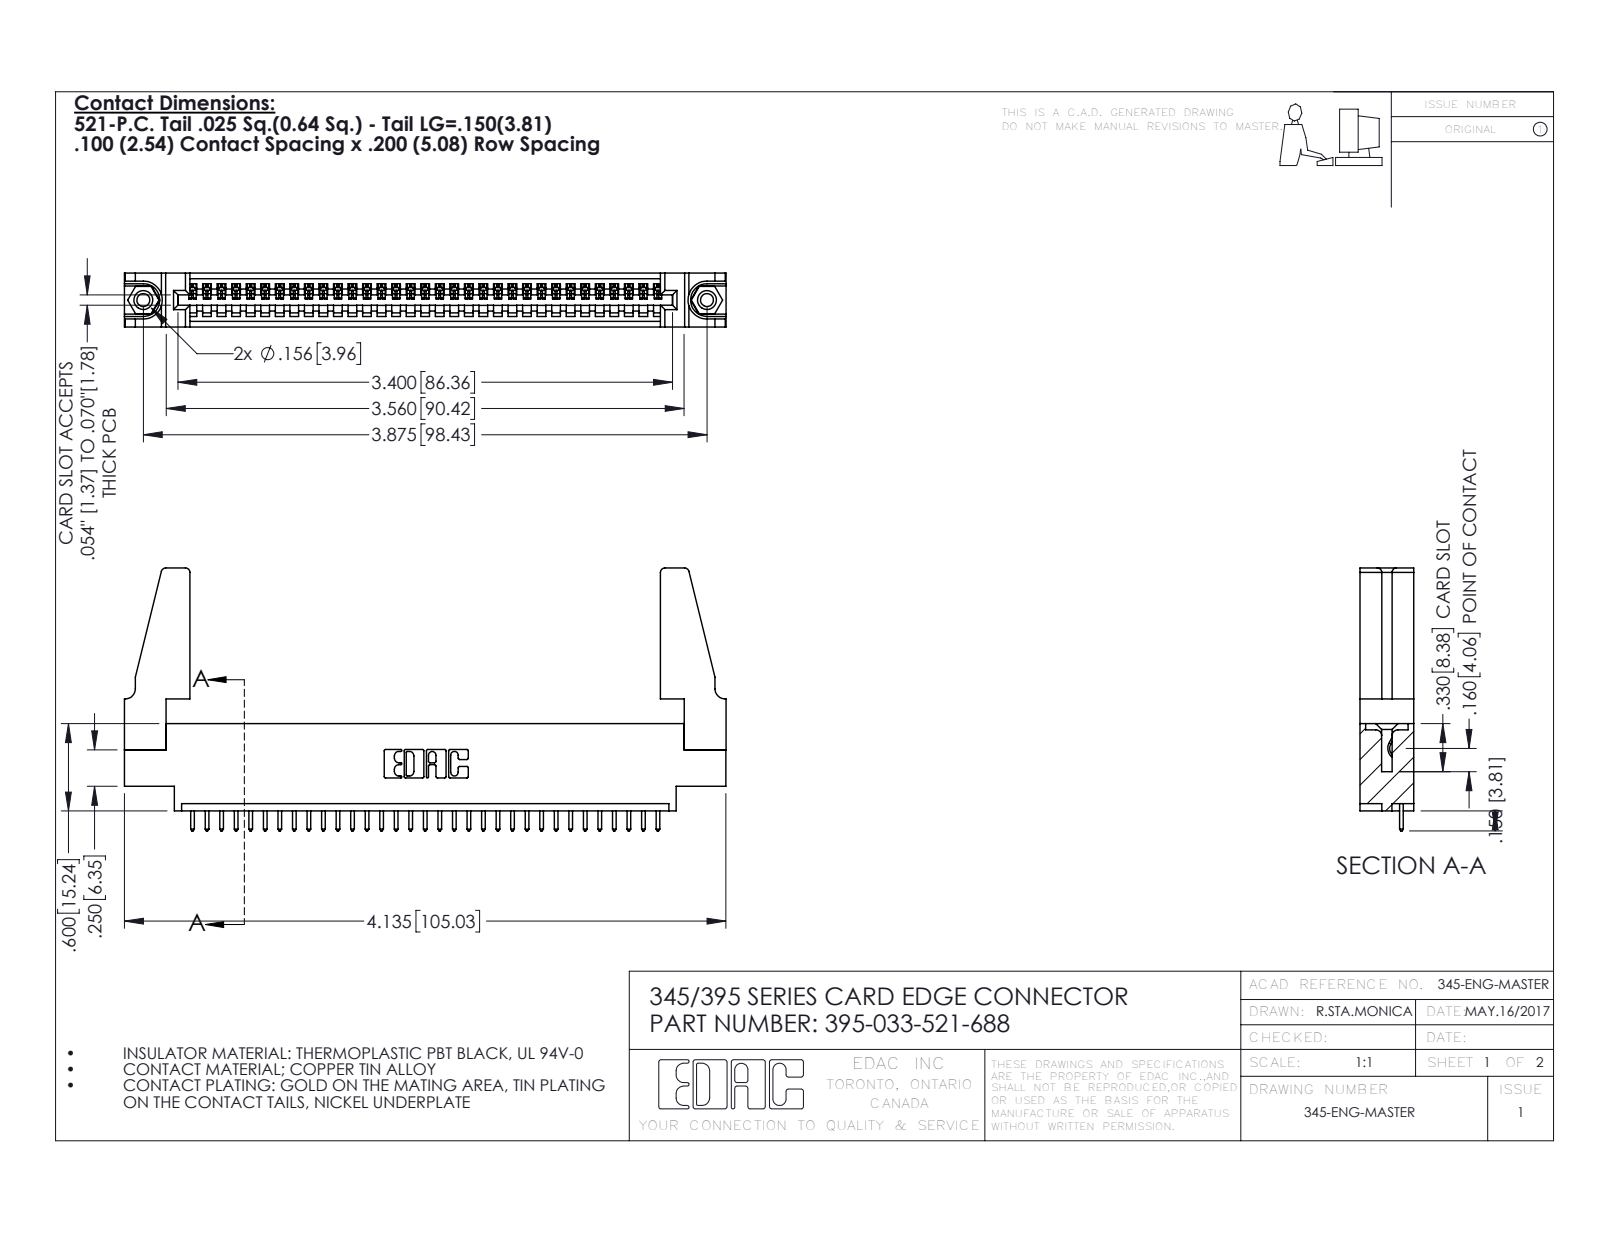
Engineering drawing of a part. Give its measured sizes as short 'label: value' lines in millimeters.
name: 395-033-521-688; 345 Part_0.170 Offset - 0.156 Dia-TH; 345-220-078_345-220-088; 345-250-001_345-250-001-102 (+1 more)
written by: SolidWorks 2016 (CONFIG_CONTROL_DESIGN)
unit: mm
bodies: 38 solids, 2168 faces (1476 planar, 676 cylindrical, 16 other)
size: 105.1 × 45.9 × 9.4
volume: 12 900 mm³; area: 15 650 mm²
holes: 2× ⌀2.3, 2× ⌀3.2, 2× ⌀4, 1× ⌀1.6
bosses: 2× ⌀3.9
rounds: 66× R0.2, 66× R0.3, 22× R0.3, 8× R0.8, 6× R0.2, 6× R0.8, 3× R0.7, 2× R0.8
face distances: 9.4, 1.8, 7.6, 5.1, 2.5, 6.9, 0.6, 5.7, 4.4, 3.8
hole spacings: 6.9, 92.5, 98.4
